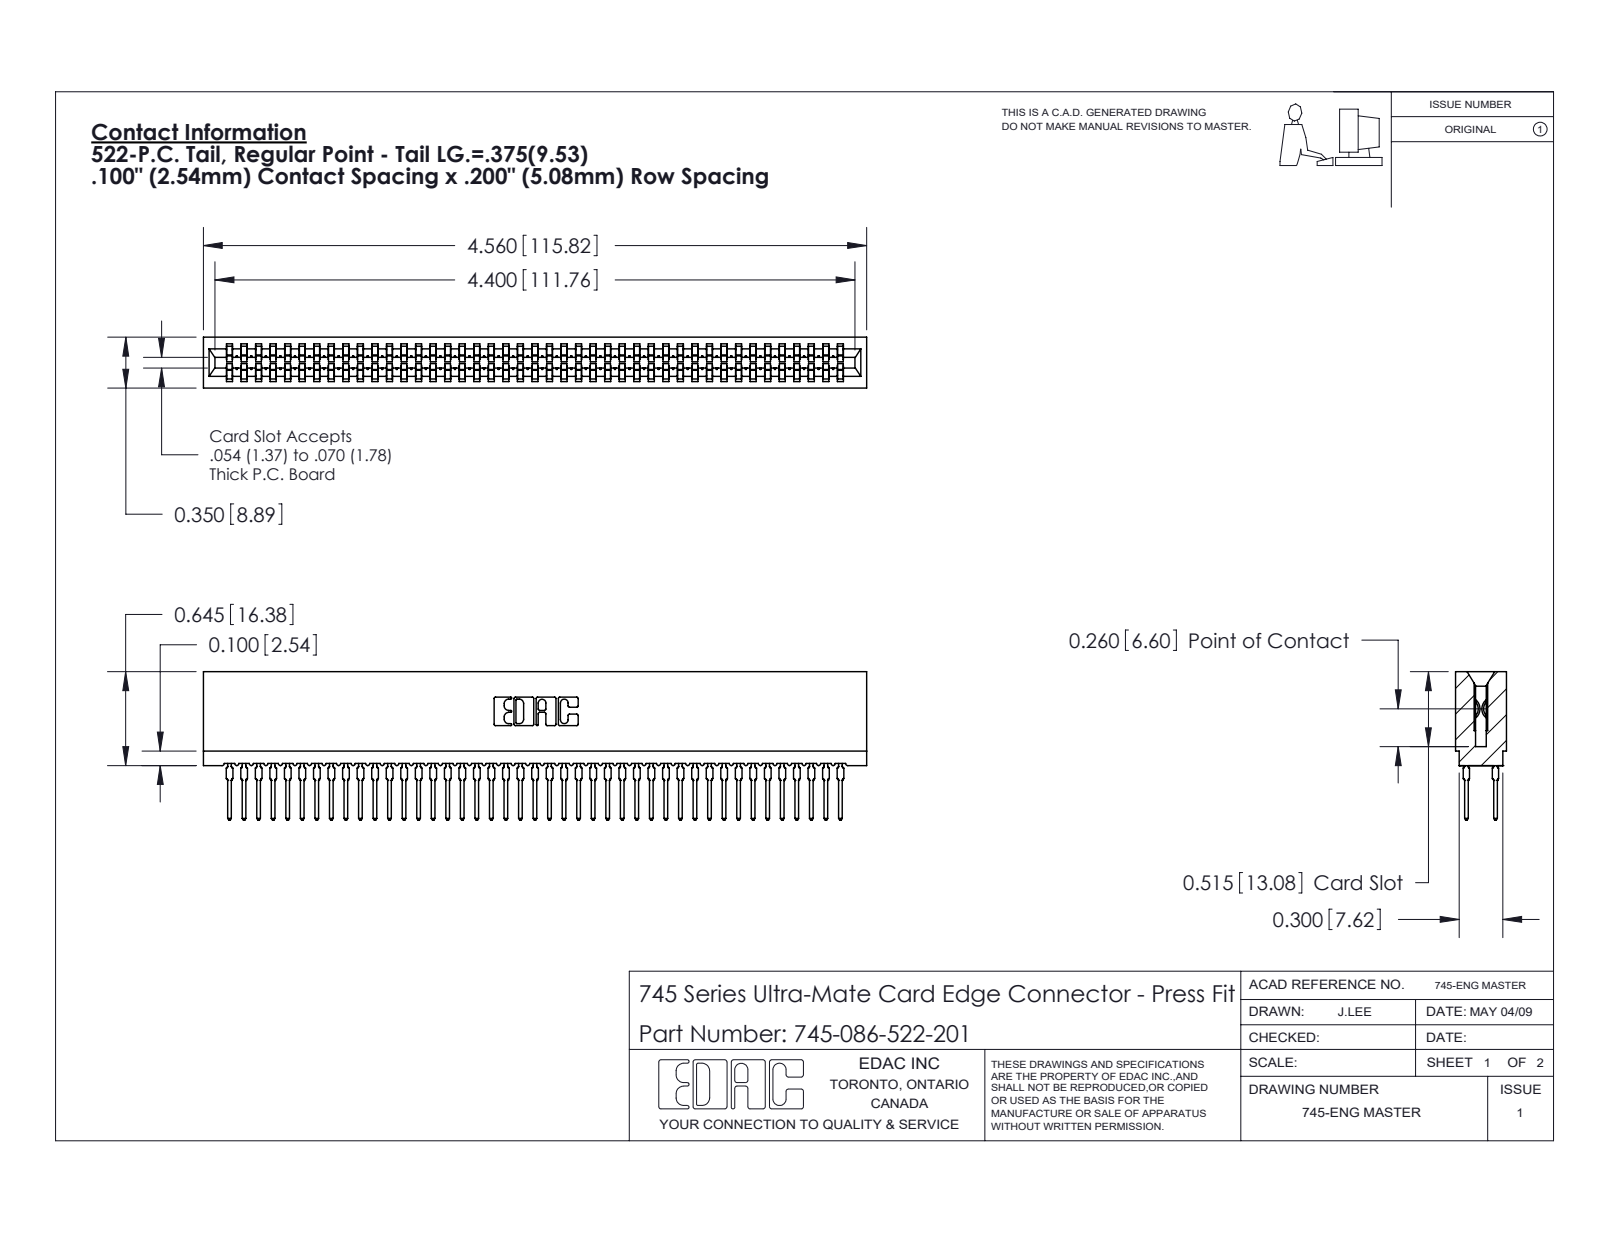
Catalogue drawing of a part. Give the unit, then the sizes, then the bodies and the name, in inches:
Units: inches
Overall size (bounding box): 4.56 × 1.021 × 0.35
Partial cylindrical surfaces — rounded edges, fillets, slot ends (radius × count): R0.021 ×172, R0.015 ×86, R0.01 ×22, R0.005 ×8, R0.011 ×8, R0.007 ×6, R0.031 ×6, R0.026 ×3
Main face-to-face distances: 0.35, 0.063, 0.287, 0.045, 0.305, 0.018, 0.243, 0.138, 0.212, 0.093
Volume: 0.642 in³ · Surface area: 33.63 in²
Bodies: 87 solids, 7792 faces (4011 planar, 1545 cylindrical, 2236 other)
Part name (STEP PRODUCT): 745-086-522-201; 745 Part_Insulator Option - 01; 745-292-001_522
STEP written by: SolidWorks 2020 (CONFIG_CONTROL_DESIGN)
